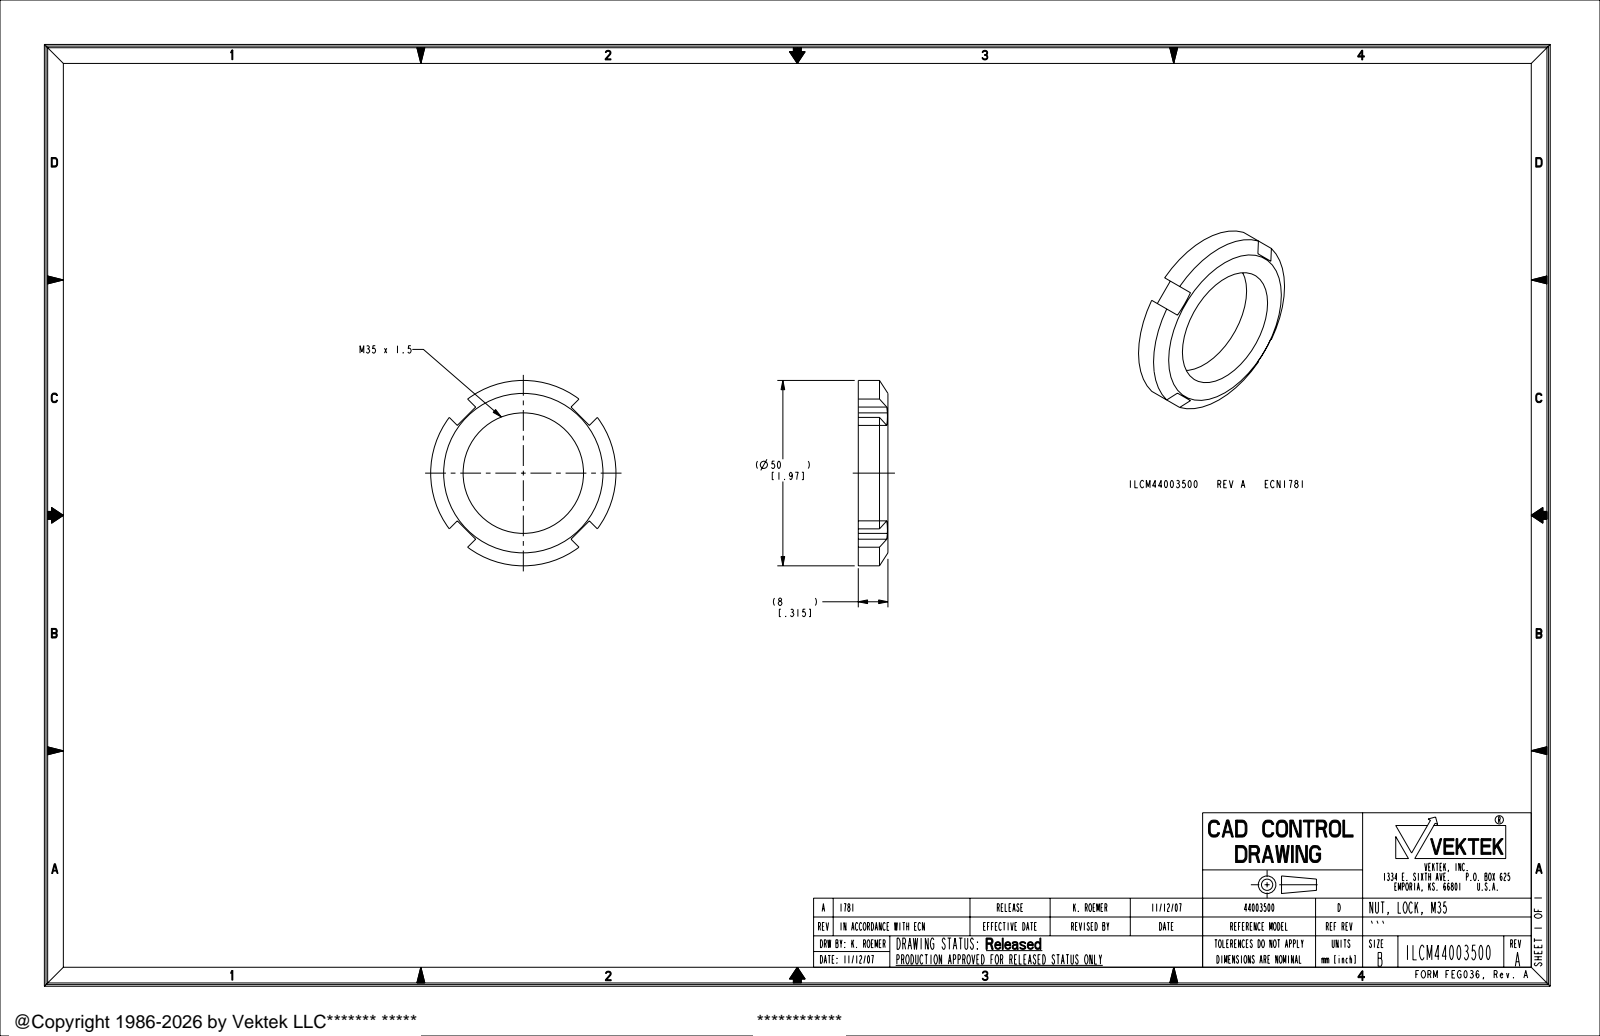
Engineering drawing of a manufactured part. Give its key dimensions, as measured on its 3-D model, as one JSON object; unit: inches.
{"part_name": "ILCM44003500", "step_written_by": "PRO/ENGINEER BY PARAMETRIC TECHNOLOGY CORPORATION, 2005180 (AUTOMOTIVE_DESIGN_CC2)", "units": "inches", "bodies": {"solids": 1, "faces": 22, "planar": 14, "cylindrical": 6, "other": 2}, "overall_size": [1.969, 1.969, 0.315], "volume_in3": 0.48, "surface_area_in2": 6.366, "round_holes": [[1.28, 1]], "round_bosses_or_shafts": [[1.969, 1]], "face_to_face_distances": [0.315, 0.717, 0.992, 1.709, 0.276]}
